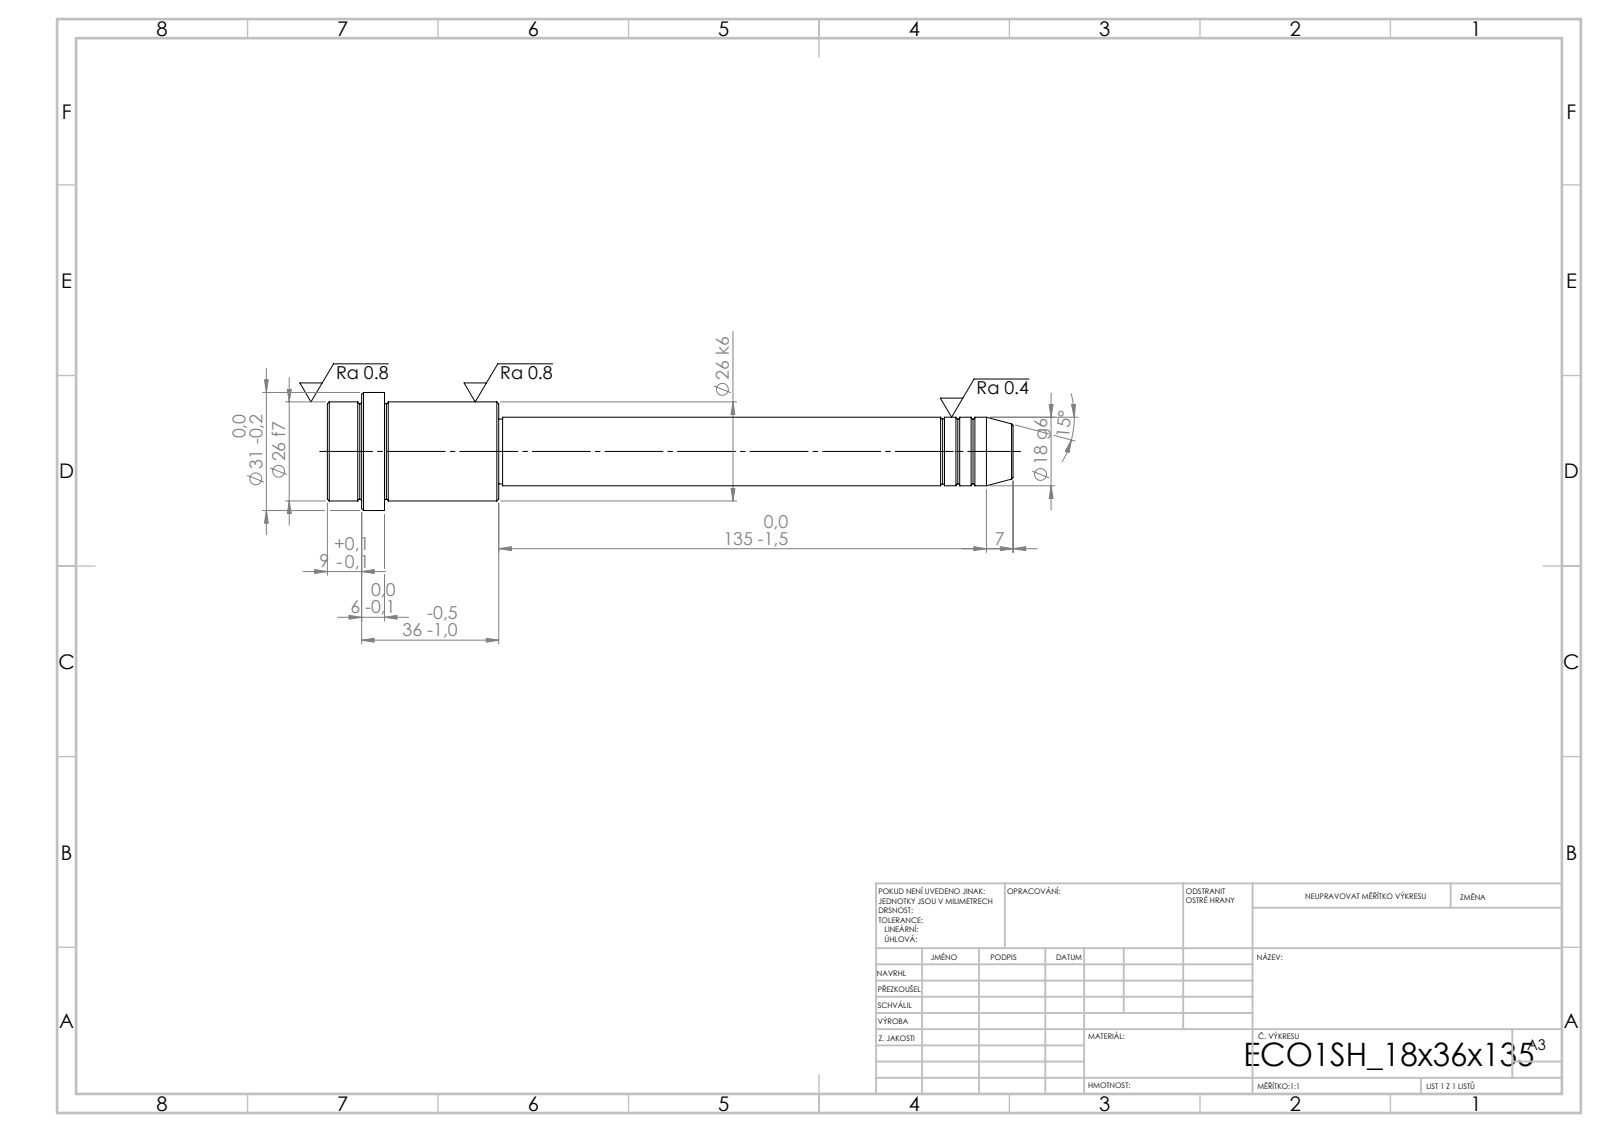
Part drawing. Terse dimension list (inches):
written by: SolidWorks 2019 (CONFIG_CONTROL_DESIGN)
unit: in
bodies: 1 solid, 52 faces (6 planar, 16 cylindrical, 30 other)
size: 7.087 × 1.22 × 1.22
volume: 3.604 in³; area: 20.05 in²
bosses: 1× ⌀1.22, 1× ⌀1.024, 1× ⌀0.709, 1× ⌀0.669
face distances: 1.772, 1.181, 0.591, 1.417, 0.236, 0.354, 5.315, 6.496, 6.732, 7.087
